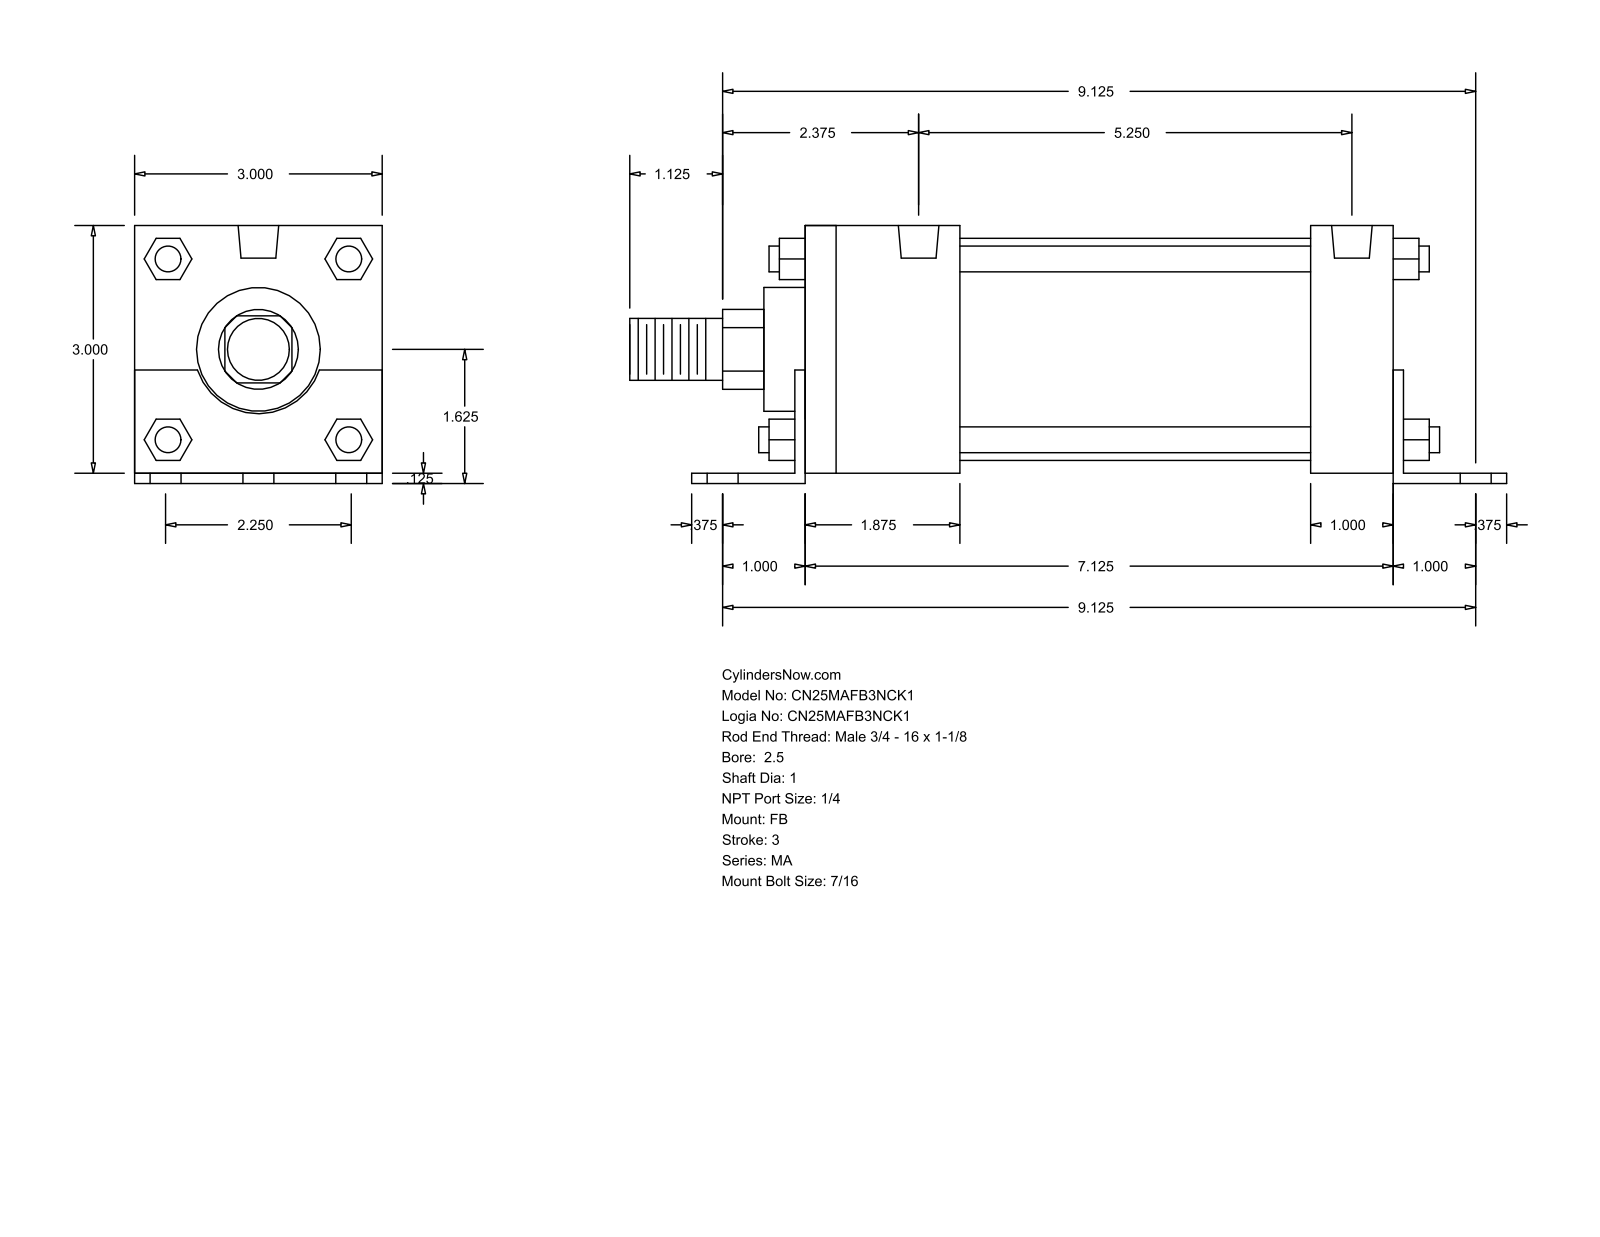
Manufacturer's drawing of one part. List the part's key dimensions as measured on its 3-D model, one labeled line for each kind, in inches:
Part name (STEP PRODUCT): MA_FB__0250_1
STEP written by: GSSL Pune (CONFIG_CONTROL_DESIGN)
Units: inches
Bodies: 0 solids, 140 faces (105 planar, 35 cylindrical, 0 other)
Overall size (bounding box): 10.625 × 3.125 × 3
Round holes (diameter × count): ⌀0.437 ×6, ⌀0.313 ×4, ⌀0.492 ×2
Round bosses / shafts (diameter × count): ⌀0.313 ×4, ⌀2.69 ×1, ⌀1.5 ×1, ⌀1 ×1, ⌀0.75 ×1
Partial cylindrical surfaces — rounded edges, fillets, slot ends (radius × count): R0.484 ×1, R0.78 ×1
Main face-to-face distances: 3, 0.125, 3.125, 7.25, 7.125, 0.5, 2, 1.875, 5.25, 5.375
Hole centre spacings: 1.125, 9.194, 9.125, 1.875, 2.25, 2.628, 5.25, 6.843
